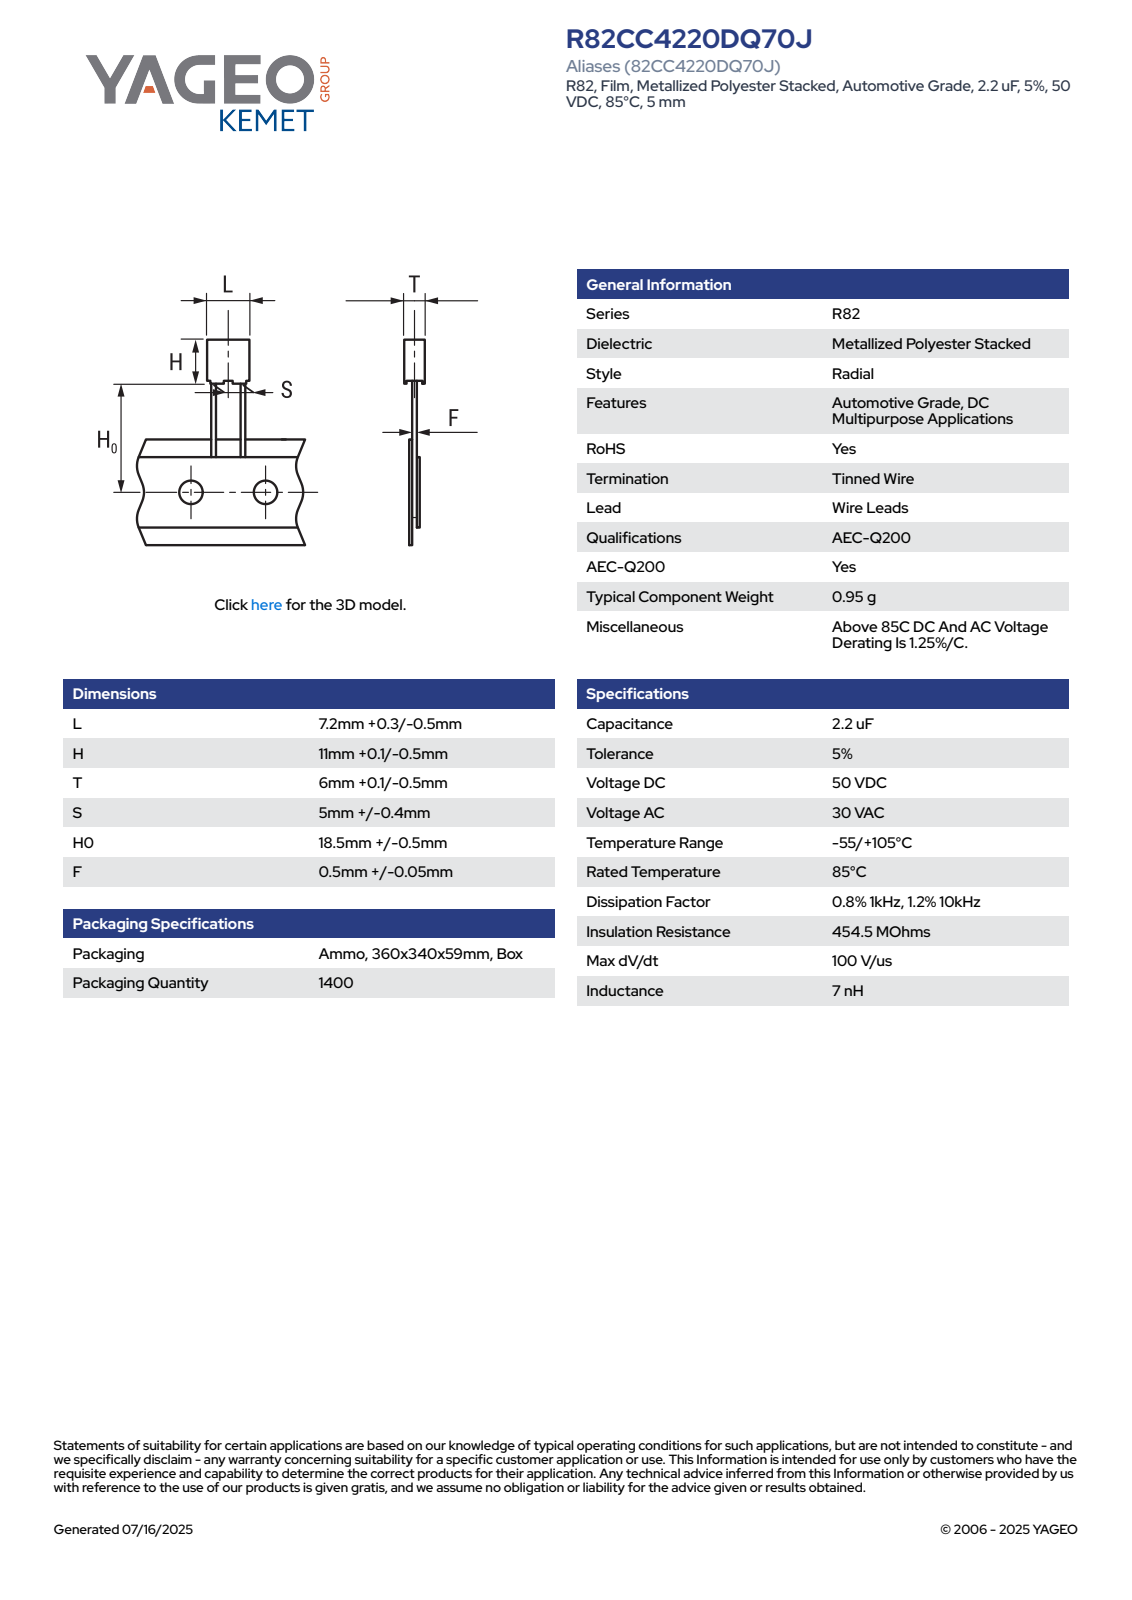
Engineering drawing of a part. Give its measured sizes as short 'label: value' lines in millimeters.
name: CFR_RB3_7.2X11X6_L7.5H11.1T6.1S5H019F0.55
written by: SolidWorks 2014 (AUTOMOTIVE_DESIGN)
unit: mm
bodies: 4 solids, 85 faces (77 planar, 8 cylindrical, 0 other)
size: 30.1 × 7.5 × 6.11
volume: 486 mm³; area: 476 mm²
bosses: 2× ⌀0.55
rounds: 4× R0.5
face distances: 6.1, 7.5, 10.35, 5.85, 7.25, 0.75, 11.1, 5.6, 7, 0.38
